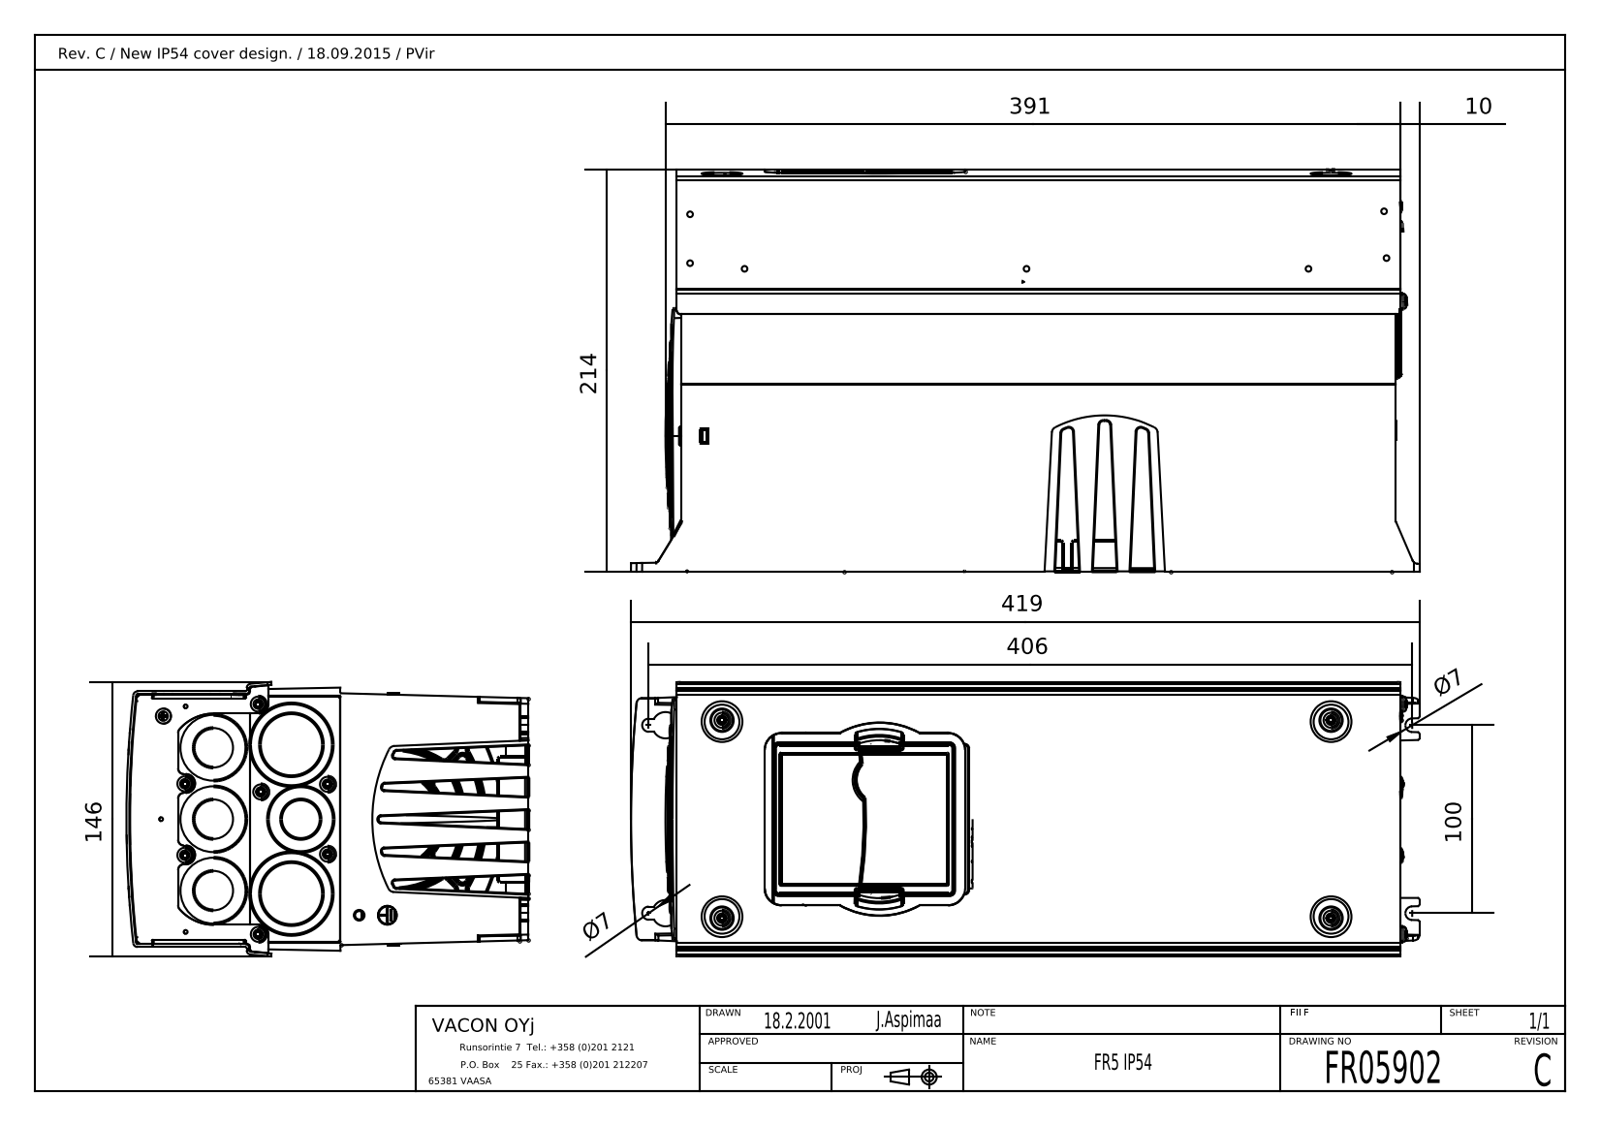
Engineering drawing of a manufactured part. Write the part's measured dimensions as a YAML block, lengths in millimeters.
part_name: "VACON_FR5_IP54_SB"
step_written_by: "CREO PARAMETRIC BY PTC INC, 2018070 (CONFIG_CONTROL_DESIGN)"
units: millimeters
bodies: {solids: 1, faces: 775, planar: 354, cylindrical: 294, other: 127}
overall_size: [419.49, 214.84, 146]
volume: 10830000
surface_area: 549518
round_holes:
  - {diameter: 3.3, count: 9}
  - {diameter: 5.4, count: 9}
  - {diameter: 6.4, count: 6}
  - {diameter: 2.5, count: 4}
  - {diameter: 3.1, count: 2}
  - {diameter: 33.5, count: 2}
  - {diameter: 37, count: 2}
  - {diameter: 3.31, count: 1}
  - {diameter: 21, count: 1}
  - {diameter: 28.3, count: 1}
round_bosses_or_shafts:
  - {diameter: 7.7, count: 5}
  - {diameter: 5.4, count: 3}
  - {diameter: 44, count: 2}
  - {diameter: 37, count: 2}
  - {diameter: 7.8, count: 2}
  - {diameter: 5.5, count: 2}
  - {diameter: 5, count: 2}
  - {diameter: 35, count: 1}
partial_cylinders:
  - {radius: 0.5, count: 22}
  - {radius: 2, count: 20}
  - {radius: 0.3, count: 14}
  - {radius: 1, count: 11}
  - {radius: 2.25, count: 10}
  - {radius: 0.75, count: 8}
  - {radius: 5, count: 8}
  - {radius: 3, count: 7}
face_to_face_distances: [1.25, 148.15, 149.4, 136, 379.56, 1.5, 1, 0.54, 380.1, 1.48]
hole_center_spacings: [40.65, 12.81, 17.02, 32.32, 39.91, 47.37, 50, 50.94]
